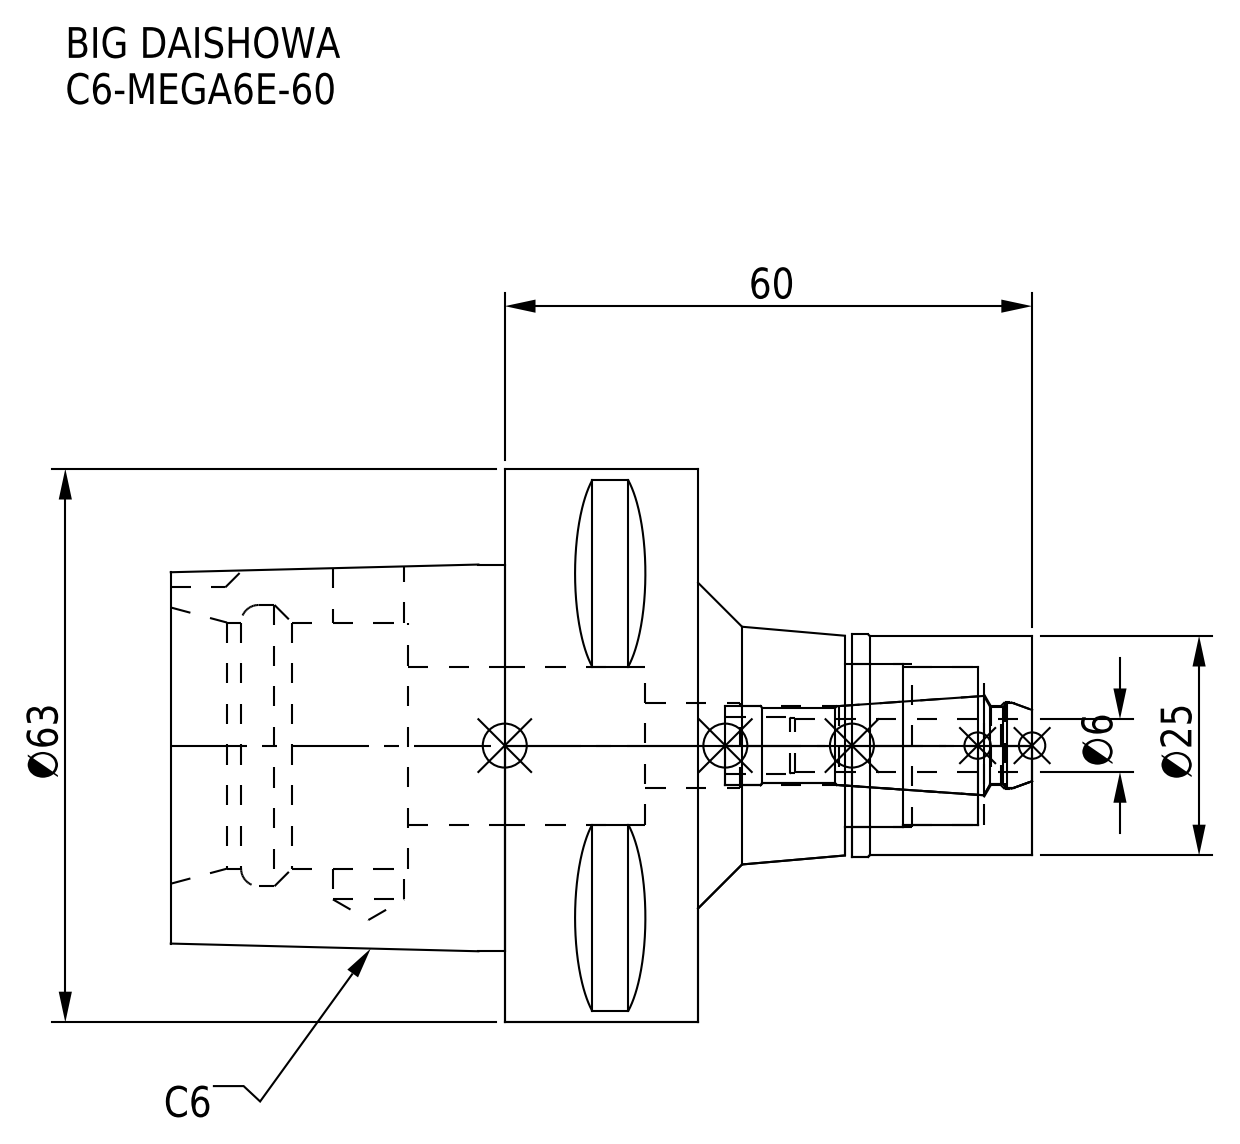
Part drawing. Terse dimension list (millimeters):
name: MEN6_1.stp; DXF_TEMP_ASSY_ASM_4_ASM.stp; C6-MEGA6E-60-060_ASM.stp; C6-MEGA6E-60_1.stp (+3 more)
written by: SolidWorks 2019 (CONFIG_CONTROL_DESIGN)
unit: mm
bodies: 2 solids, 94 faces (35 planar, 35 cylindrical, 24 other)
size: 98 × 63 × 63
volume: 113 829 mm³; area: 26 583 mm²
holes: 1× ⌀8.1, 1× ⌀9, 1× ⌀9.6, 1× ⌀9.9, 1× ⌀18, 1× ⌀18.5, 1× ⌀28, 1× ⌀32
bosses: 1× ⌀63, 1× ⌀25.3, 1× ⌀25
rounds: 1× R5
face distances: 22, 38, 60, 27, 98, 71, 33, 11, 24.89, 55.4
